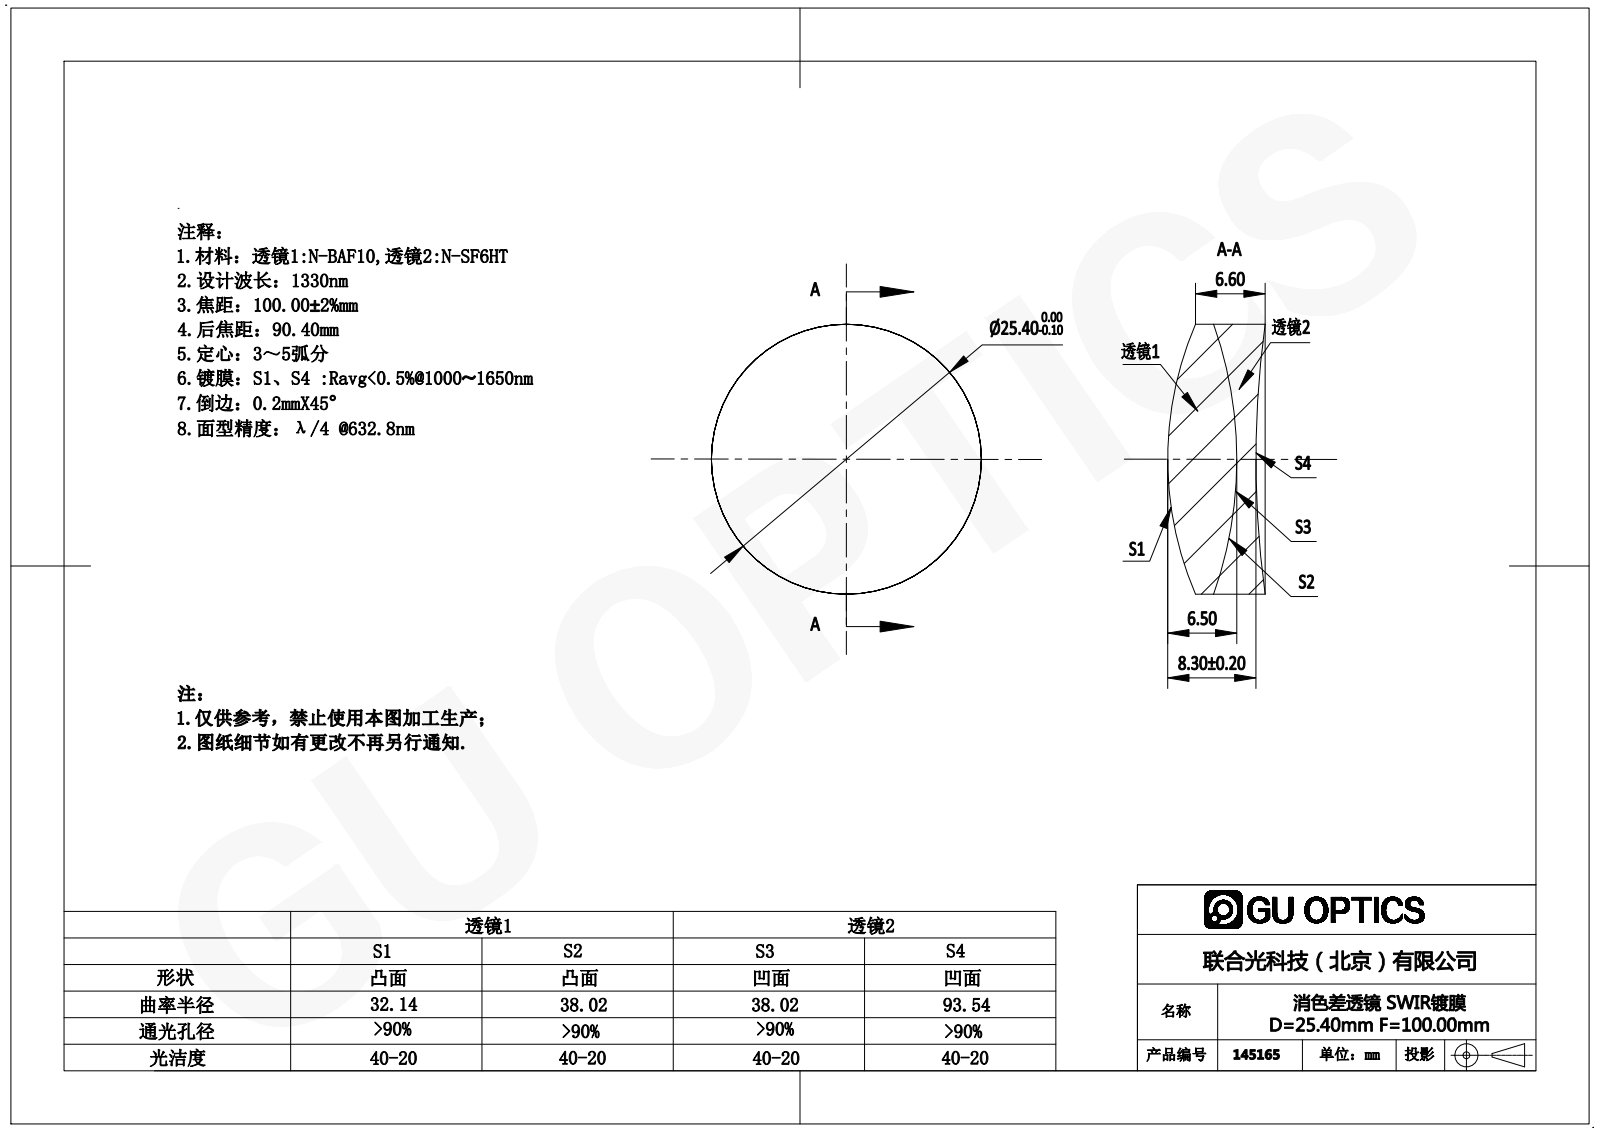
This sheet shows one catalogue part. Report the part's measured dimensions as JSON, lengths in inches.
{"part_name": "145165", "step_written_by": "SolidWorks 2016 (AUTOMOTIVE_DESIGN)", "units": "inches", "bodies": {"solids": 2, "faces": 12, "planar": 0, "cylindrical": 4, "other": 8}, "overall_size": [1, 1, 0.361], "volume_in3": 0.23, "surface_area_in2": 4.035, "round_bosses_or_shafts": [[1, 1]]}
